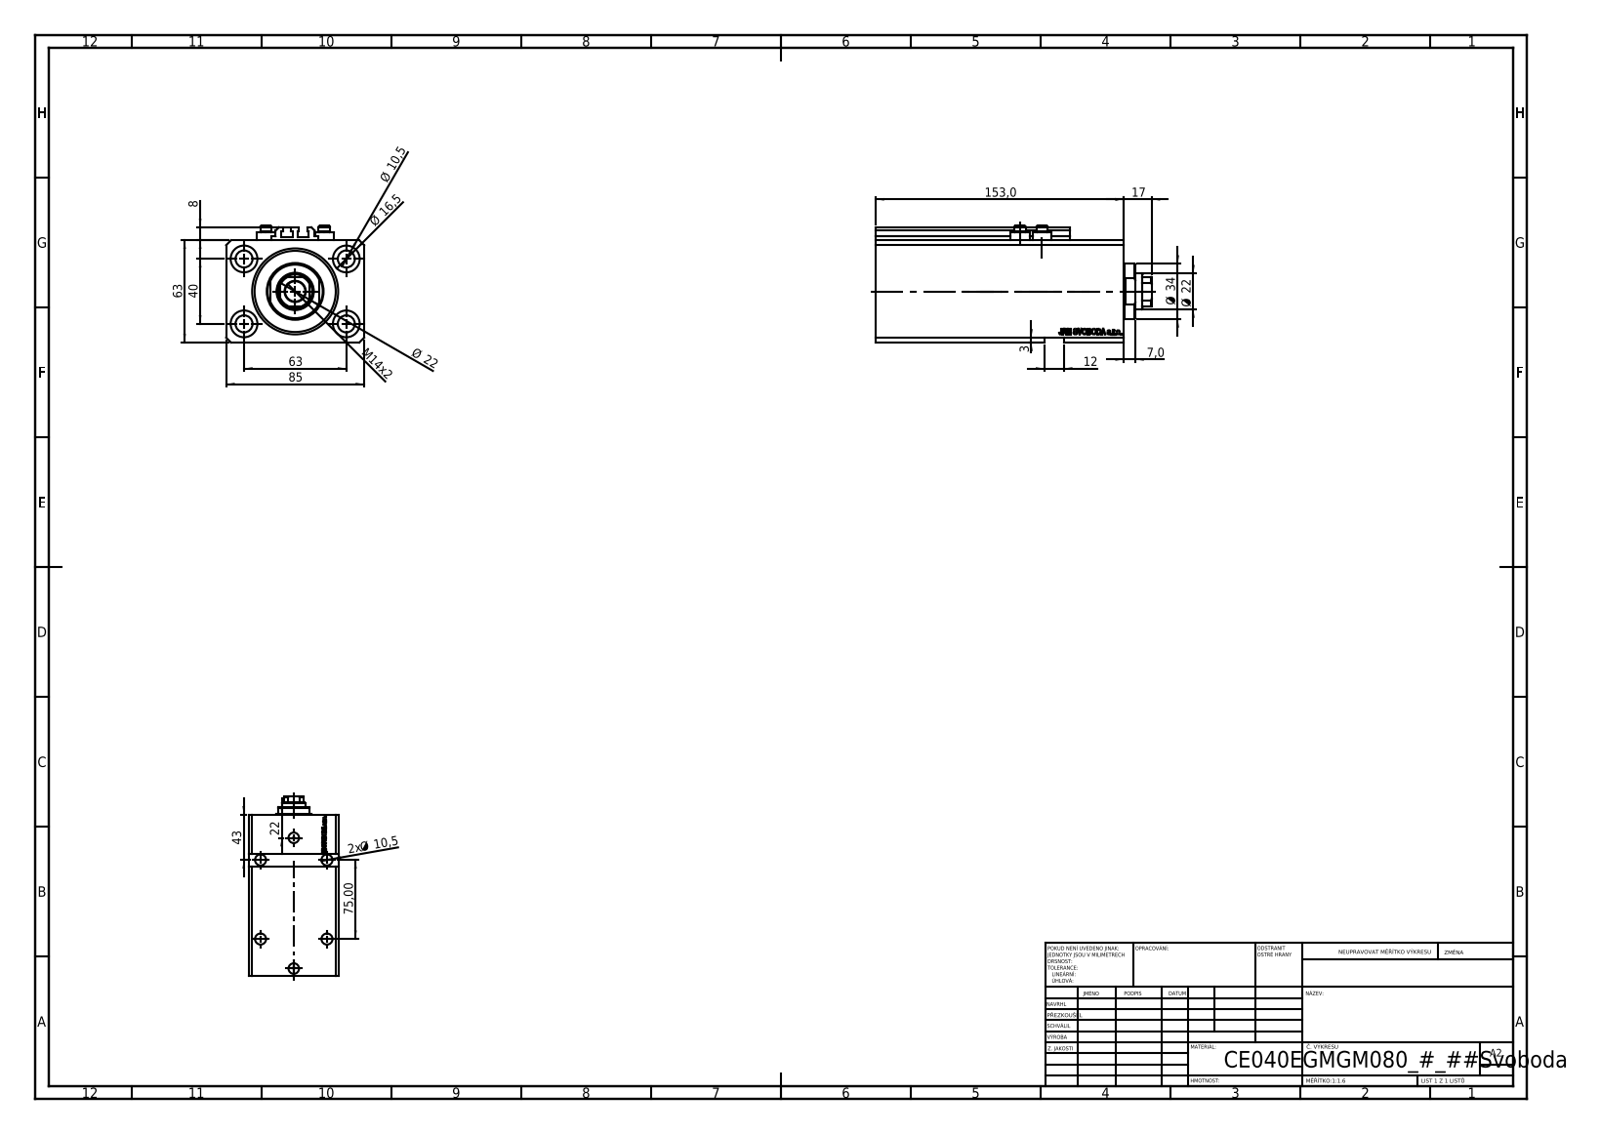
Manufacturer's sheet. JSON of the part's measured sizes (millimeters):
{"part_name": "V250CE_E_Body; V250CE_C_VCP; ALLEN BOLT V250CE; V250CE_VC_E", "step_written_by": "SolidWorks 2019 (CONFIG_CONTROL_DESIGN)", "units": "millimeters", "bodies": {"solids": 8, "faces": 1107, "planar": 535, "cylindrical": 146, "other": 426}, "overall_size": [170, 85, 72], "volume_mm3": 683849, "surface_area_mm2": 140822, "round_holes": [[10.5, 8], [1.25, 4], [4, 4], [16.5, 4], [10, 2], [13.16, 2], [20, 2], [12.5, 1], [22, 1], [40, 1], [53, 1]], "round_bosses_or_shafts": [[11.6, 4], [7, 4], [34, 1]], "partial_cylinders_radius": [[0.2, 10], [10.5, 1]], "face_to_face_distances": [63, 85, 153, 17, 136, 11.4, 124.6, 141.6, 3, 65], "hole_center_spacings": [37.31, 63, 13.6, 15.4, 24.96, 33.62, 36, 37.86]}
